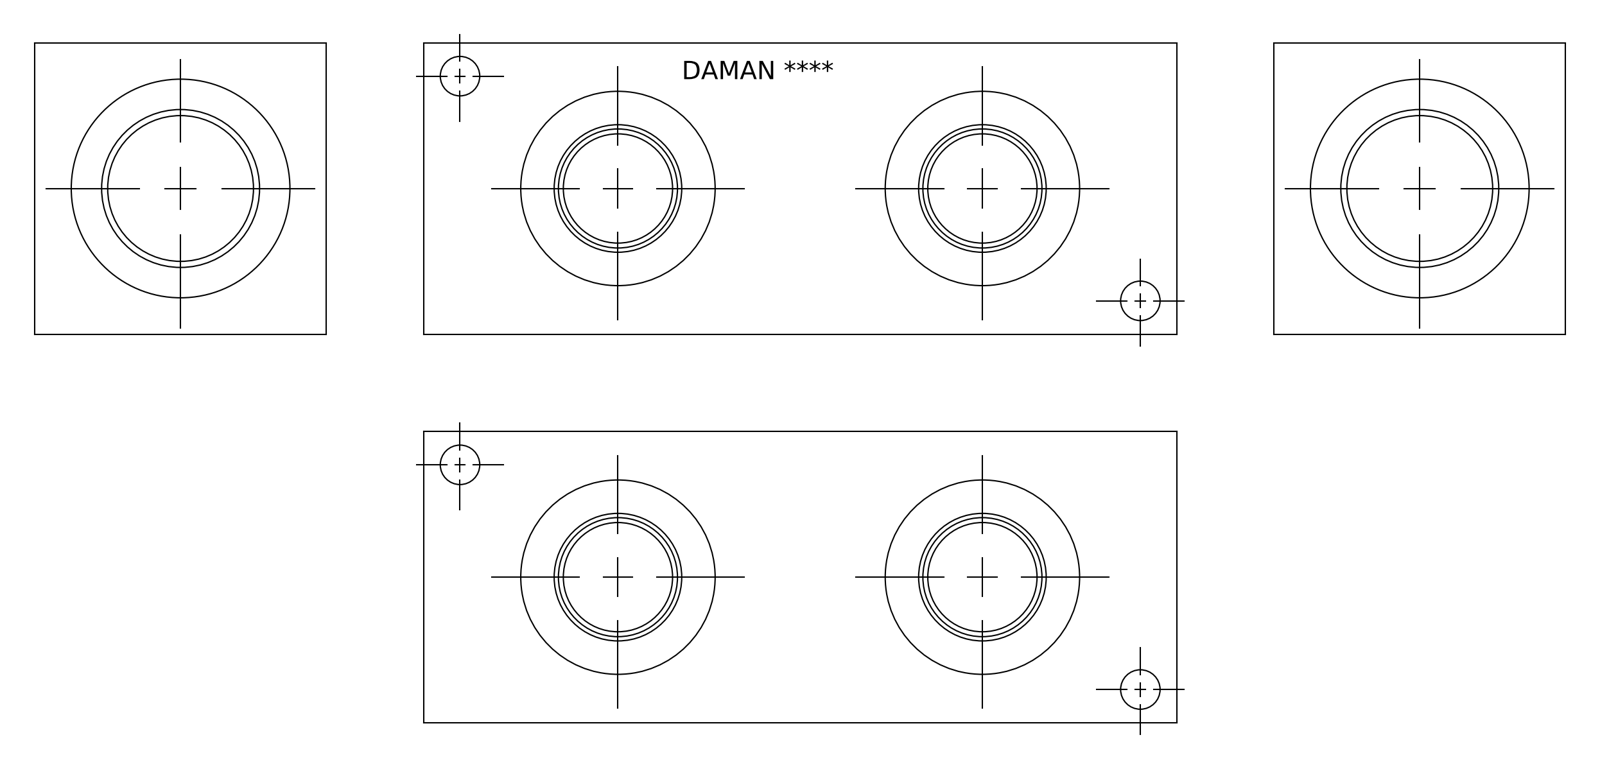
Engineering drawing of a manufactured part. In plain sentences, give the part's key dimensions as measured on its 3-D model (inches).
The part is named "Part_+H0900216S_3D". Its 3-D file was written by "Autodesk Inventor 2020 (AUTOMOTIVE_DESIGN)". It is 1 solid with 414 faces: 222 planar, 45 cylindrical and 147 other. Overall it measures 7.75 by 3 by 3 inches. Its volume is 55.31 cubic inches and its surface area 153 square inches. Round holes: 4 of diameter 0.406, 4 of diameter 1.231, 4 of diameter 1.329, 4 of diameter 1.934, 3 of diameter 1.313, 3 of diameter 1.398, 1 of diameter 1.313, 1 of diameter 1.5, 1 of diameter 1.544, 1 of diameter 1.625, 1 of diameter 1.625, 1 of diameter 1.644. Partial cylindrical surfaces (rounded edges, fillets, slot ends): 4 of radius 0.563. The main face-to-face distances are 3, 0.031, 2.969, 7.75, 7.719, 7.688, 0.781, 0.75, 2.219, 6.969. The hole center spacings are 1.994, 5.498, 3.75, 7.372.
